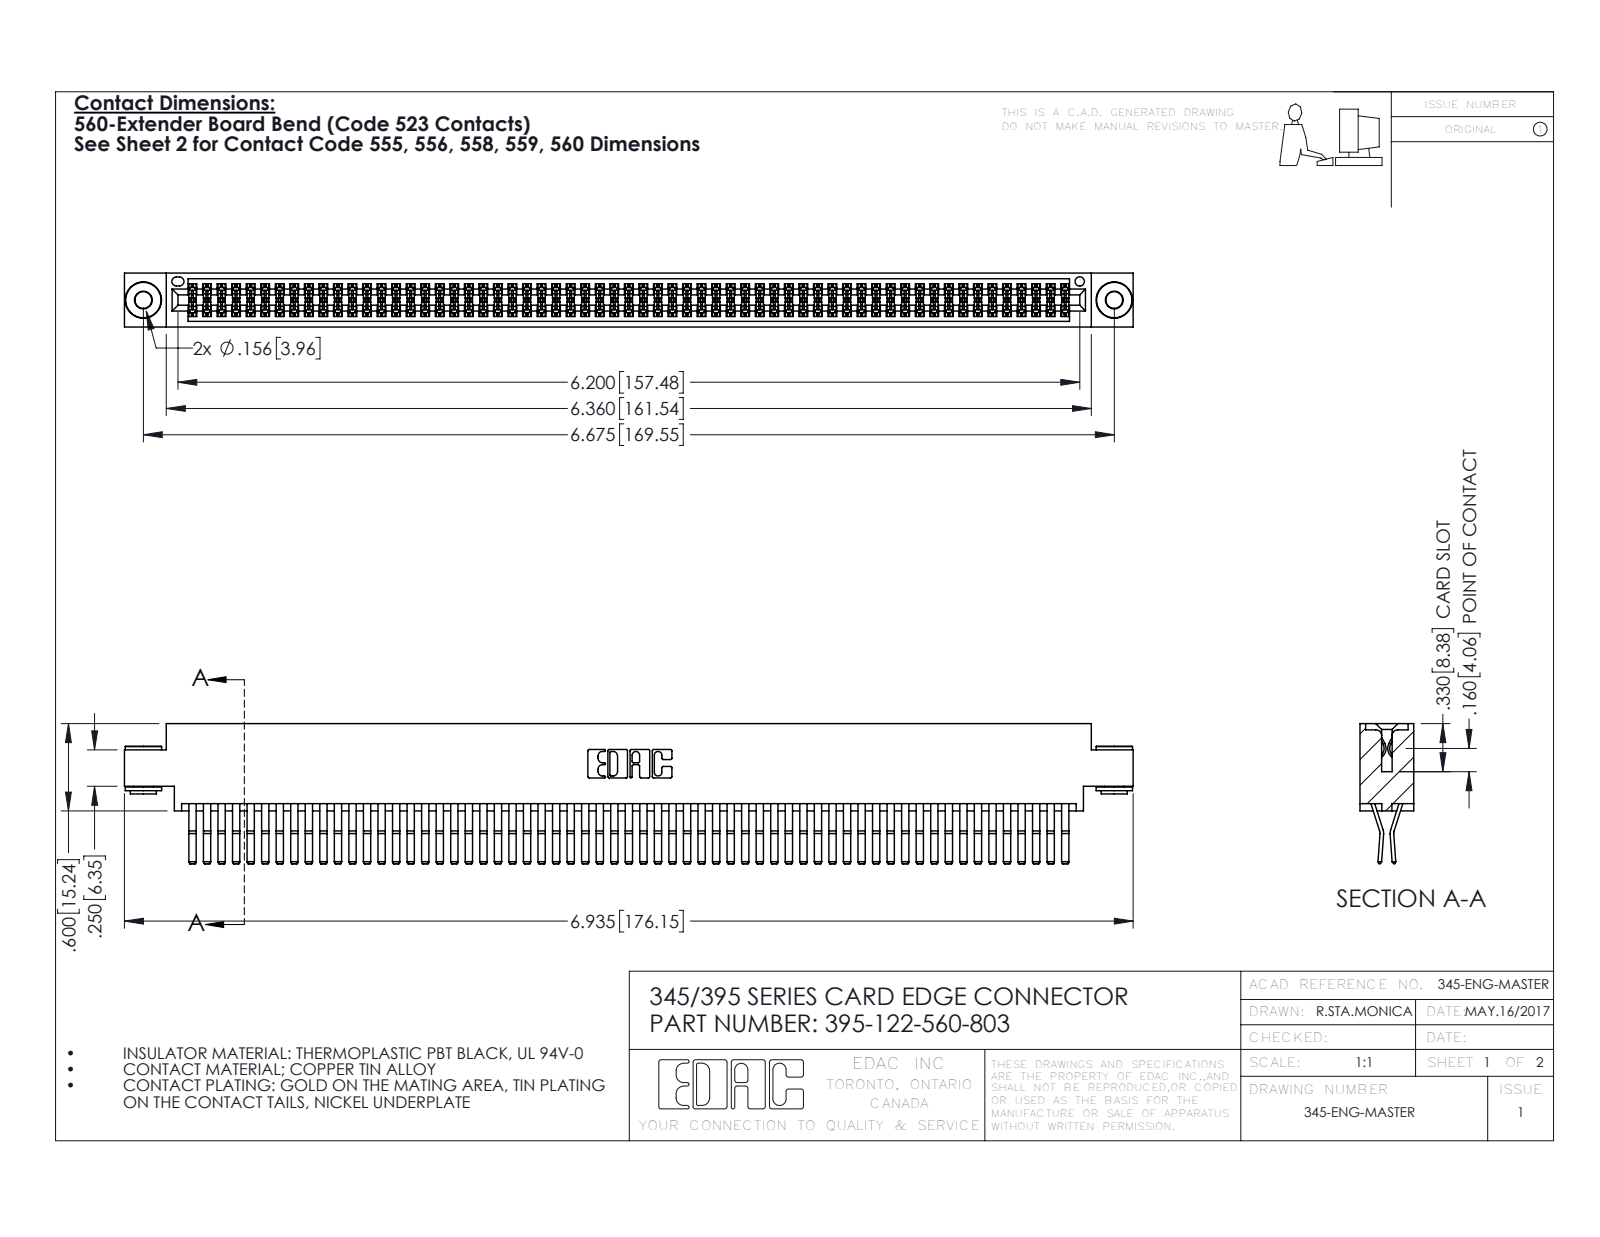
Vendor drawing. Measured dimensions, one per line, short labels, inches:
name: 345-250-002_345-250-002-102; 345 Part_0.170 Offset - 0.156 Dia-TH; 345-292-001_560 Tail; 395-122-560-803
written by: SolidWorks 2016 (CONFIG_CONTROL_DESIGN)
unit: in
bodies: 125 solids, 6512 faces (4120 planar, 2384 cylindrical, 8 other)
size: 6.935 × 0.962 × 0.37
volume: 1.098 in³; area: 45.52 in²
holes: 2× ⌀0.116, 2× ⌀0.156, 1× ⌀0.064
bosses: 2× ⌀0.25, 2× ⌀0.18, 2× ⌀0.136
rounds: 183× R0.006, 22× R0.01, 6× R0.007, 6× R0.031, 3× R0.026, 2× R0.01, 2× R0.014, 2× R0.019
face distances: 0.025, 0.072, 0.298, 0.37, 0.2, 0.098, 0.272, 0.225, 0.175, 0.149
hole spacings: 0.27, 6.439, 6.675
